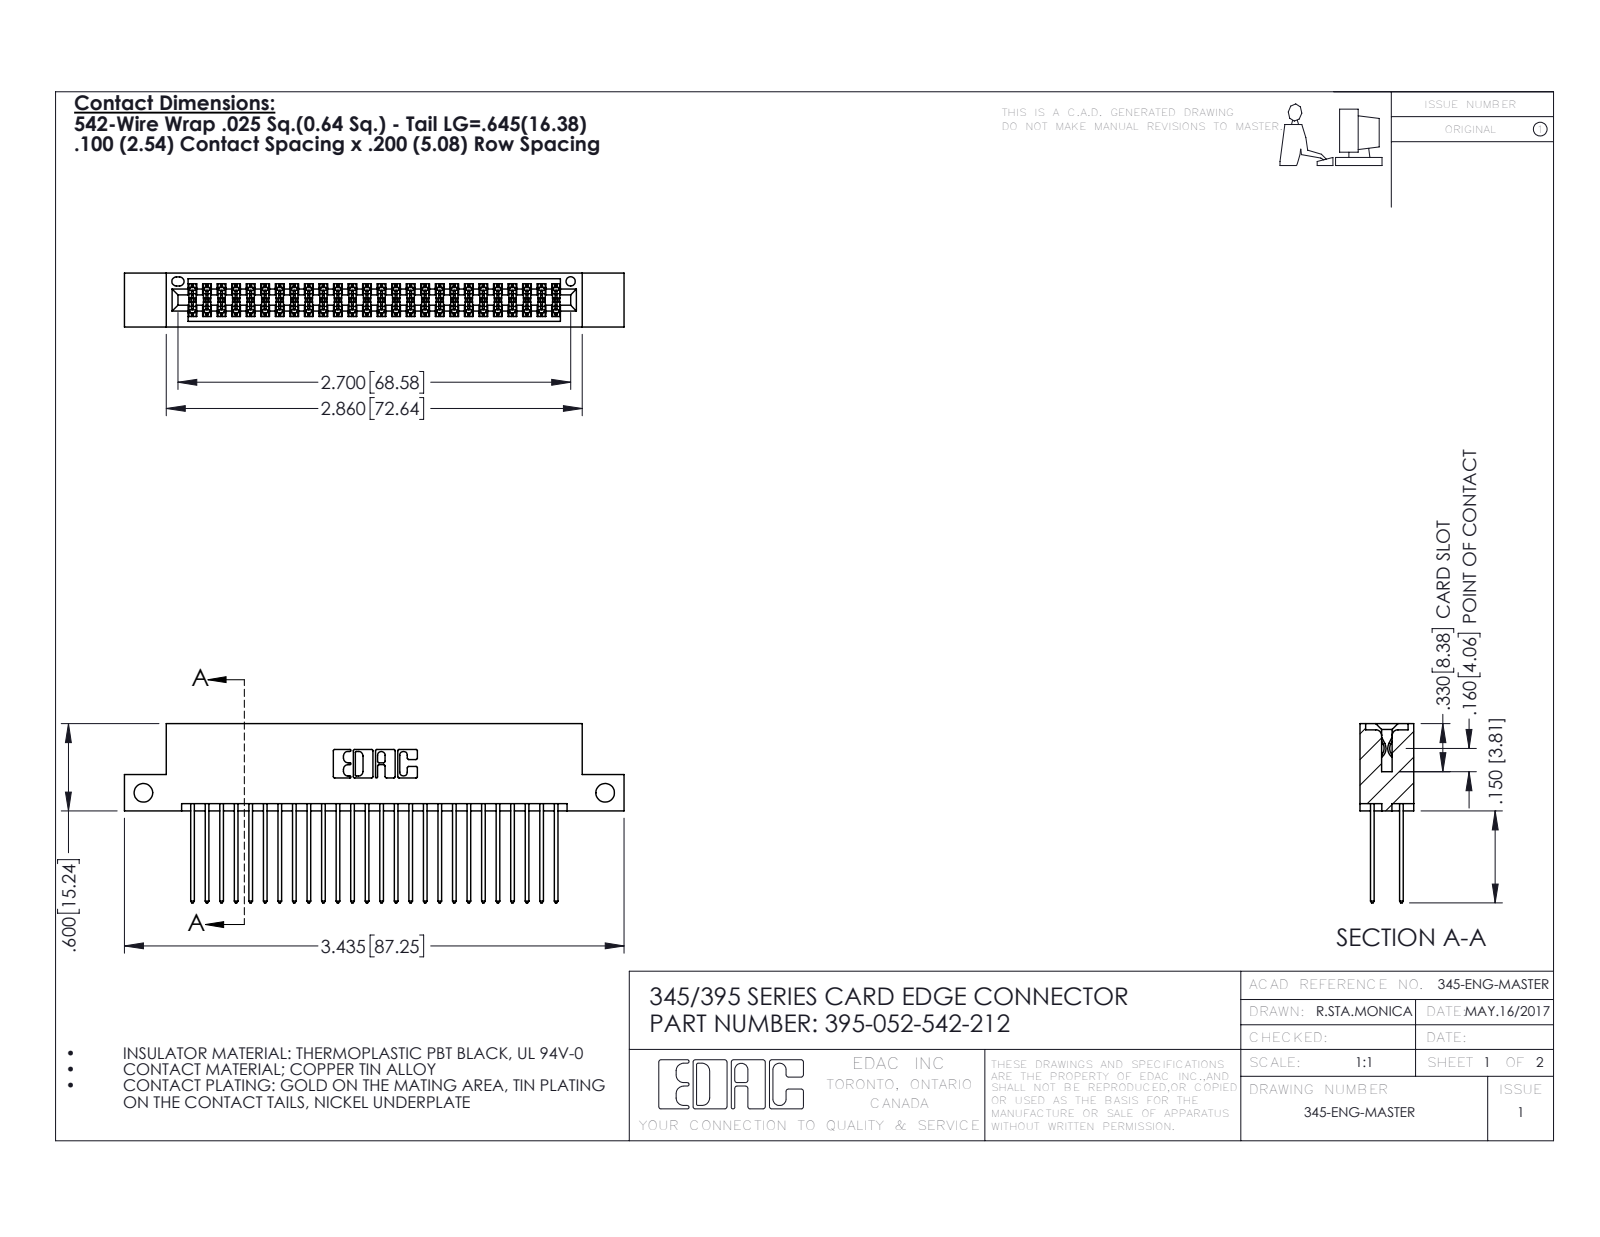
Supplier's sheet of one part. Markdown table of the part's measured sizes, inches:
| quantity | value |
| --- | --- |
| part name | 395-052-542-212; 345-292-001_345-293-142; 345 Part_Flush Mounting Lugs - Side Mount |
| STEP written by | SolidWorks 2016 (CONFIG_CONTROL_DESIGN) |
| units | inches |
| bodies | 53 solids, 2726 faces (1796 planar, 930 cylindrical, 0 other) |
| overall size | 3.435 × 1.232 × 0.37 |
| volume | 0.518 in³ |
| surface area | 20.5 in² |
| round holes (diameter × count) | 0.128 × 2, 0.064 × 1 |
| partial cylindrical surfaces (radius × count) | 0.006 × 78, 0.01 × 52, 0.01 × 22, 0.007 × 6, 0.031 × 6, 0.026 × 3, 0.014 × 2, 0.019 × 2 |
| main face-to-face distances | 0.298, 0.072, 0.2, 0.098, 0.272, 0.025, 0.37, 0.225, 0.175, 0.149 |
| hole center spacings | 3.175 |
